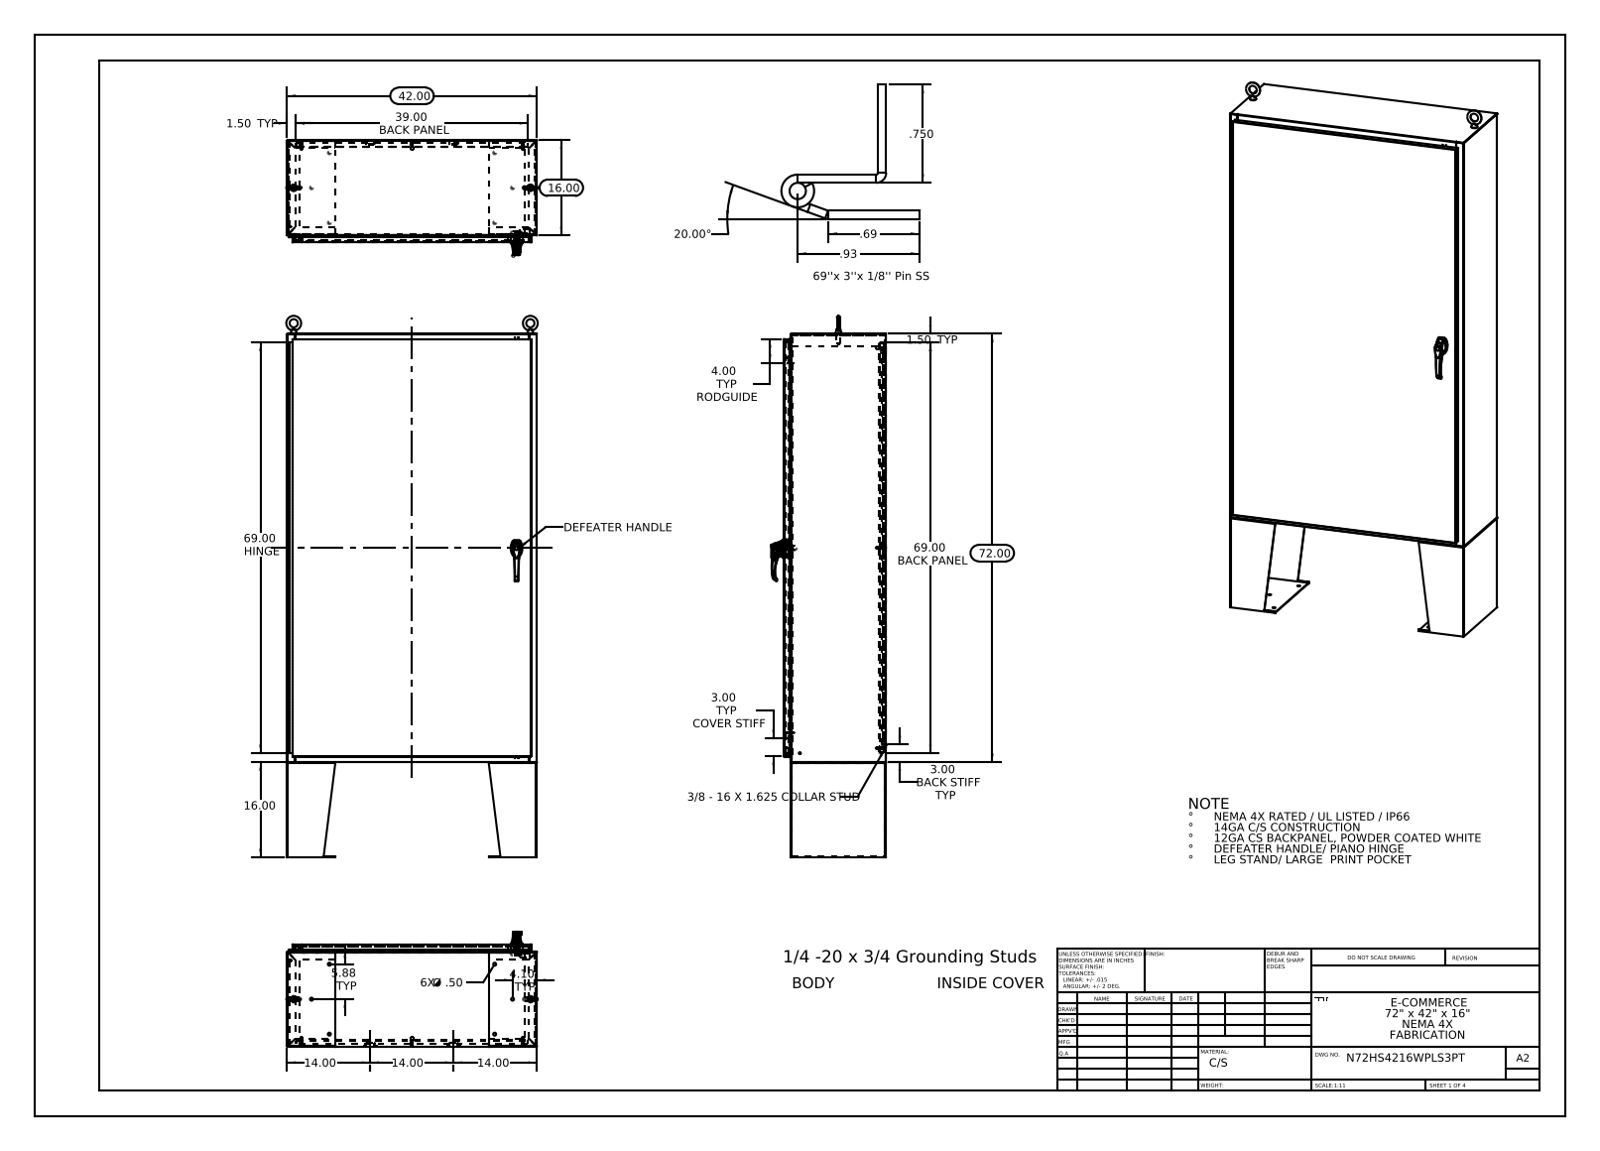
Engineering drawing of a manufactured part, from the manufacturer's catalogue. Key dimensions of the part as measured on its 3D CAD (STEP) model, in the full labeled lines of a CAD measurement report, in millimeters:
Part name (STEP PRODUCT): g26103103_26163303; N72HS4216SSWPLS3PT Hinge Enclosure Side2; 00005310_26163101; N72HS4216SSWPLS3PT Backpanel (+8 more)
STEP written by: SolidWorks 2013 (CONFIG_CONTROL_DESIGN)
Units: millimetres
Bodies: 55 solids, 4096 faces (1673 planar, 1605 cylindrical, 818 other)
Overall size (bounding box): 2311.4 × 1073.7 × 490.4
Volume: 21 010 000 mm³ · Surface area: 19 970 000 mm²
Round holes (diameter × count): ⌀12.7 ×14, ⌀6.4 ×10, ⌀19.1 ×4, ⌀3.5 ×3, ⌀4.1 ×3, ⌀2 ×2, ⌀5.2 ×2, ⌀8 ×2, ⌀11.1 ×2, ⌀3.2 ×1, ⌀3.2 ×1, ⌀5 ×1
Round bosses / shafts (diameter × count): ⌀15.9 ×10, ⌀4 ×10, ⌀3.6 ×10, ⌀9.5 ×8, ⌀8.4 ×8, ⌀8 ×3, ⌀6 ×3, ⌀30 ×1
Partial cylindrical surfaces — rounded edges, fillets, slot ends (radius × count): R3 ×37, R0.3 ×34, R0.2 ×33, R2.2 ×28, R1 ×15, R0.7 ×12, R1 ×8, R3.6 ×8
Main face-to-face distances: 1.9, 435, 2.6, 433.1, 27.3, 436.9, 25.4, 407.7, 409.6, 29.9
Hole centre spacings: 213.2, 421.1, 745.6, 796.2, 804.2, 854.1, 870.9, 976.4
